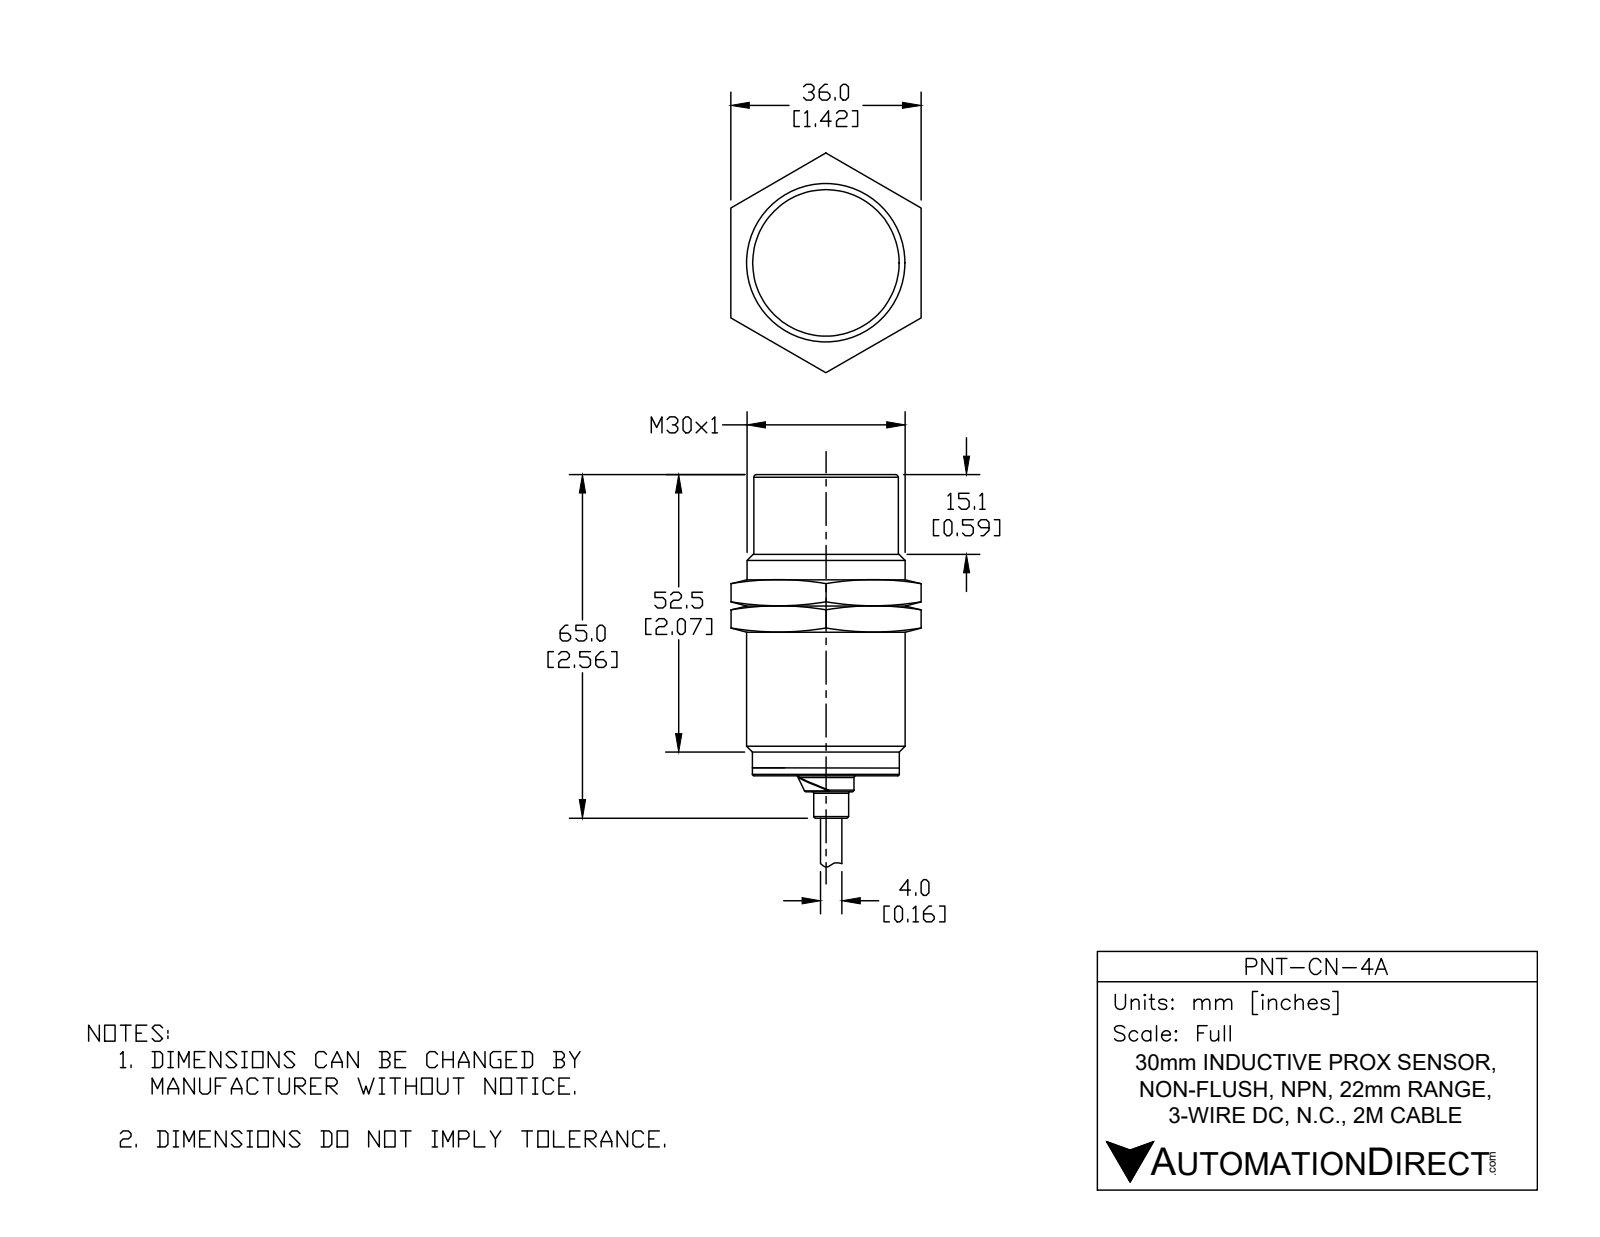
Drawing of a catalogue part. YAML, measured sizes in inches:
part_name: "PNT-CN-4A"
step_written_by: "SolidWorks 2017 (AUTOMOTIVE_DESIGN)"
units: inches
bodies: {solids: 1, faces: 74, planar: 14, cylindrical: 30, other: 30}
overall_size: [4.559, 1.181, 1.181]
volume: 2.487
surface_area: 11.9
round_holes:
  - {diameter: 0.162, count: 1}
round_bosses_or_shafts:
  - {diameter: 0.049, count: 6}
  - {diameter: 1.181, count: 1}
  - {diameter: 1.095, count: 1}
  - {diameter: 1.094, count: 1}
  - {diameter: 0.417, count: 1}
  - {diameter: 0.26, count: 1}
  - {diameter: 0.157, count: 1}
partial_cylinders:
  - {radius: 0.077, count: 1}
face_to_face_distances: [2.244, 2.362, 0.118, 2.28, 2.559, 0.315, 0.197, 4.559, 2.315, 2.197]
